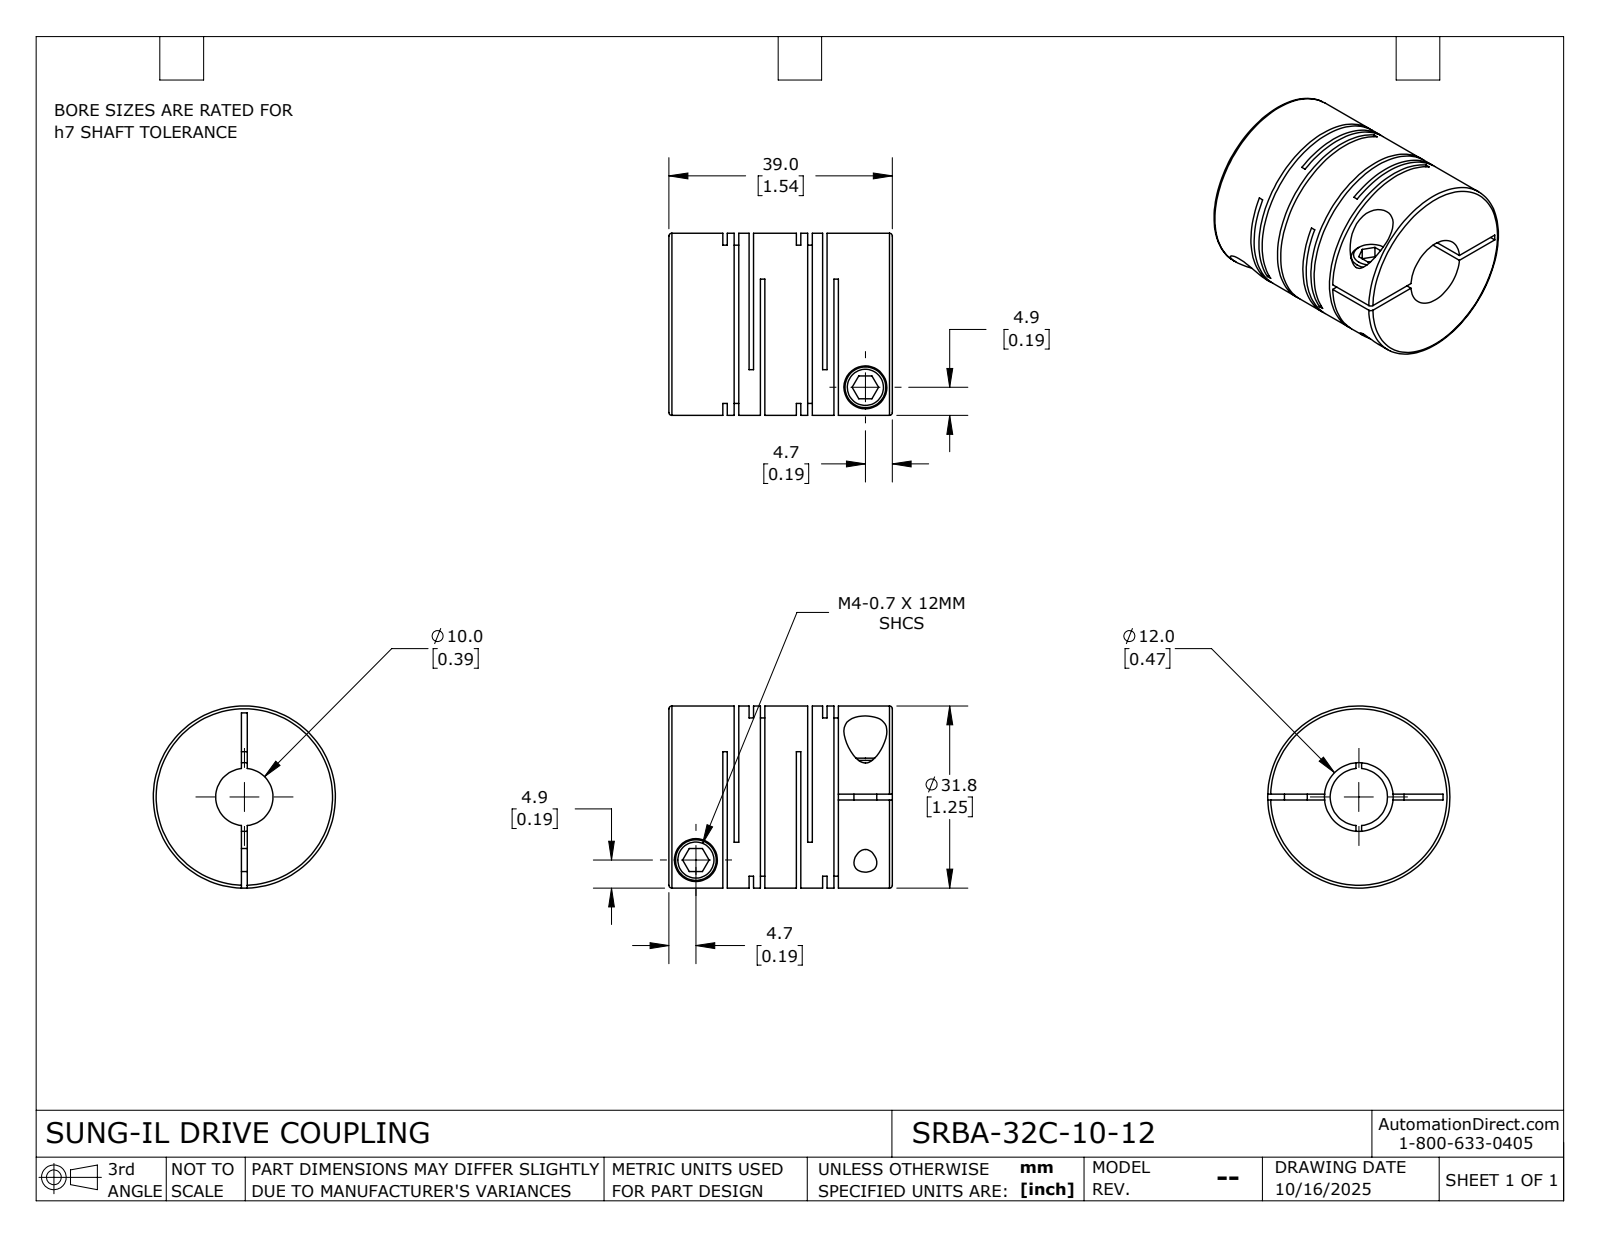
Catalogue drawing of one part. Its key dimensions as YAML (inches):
part_name: "SRBA-32C-10-12"
step_written_by: "SolidWorks 2024 (CONFIG_CONTROL_DESIGN)"
units: inches
bodies: {solids: 1, faces: 115, planar: 60, cylindrical: 42, other: 13}
overall_size: [1.535, 1.252, 1.252]
volume: 1.382
surface_area: 24.43
round_holes:
  - {diameter: 0.157, count: 2}
  - {diameter: 0.295, count: 2}
  - {diameter: 0.394, count: 1}
  - {diameter: 0.472, count: 1}
round_bosses_or_shafts:
  - {diameter: 0.28, count: 2}
  - {diameter: 1.252, count: 1}
face_to_face_distances: [0.031, 0.506, 0.078, 0.18, 0.474, 0.046, 0.428, 0.149, 0.325, 0.102]
